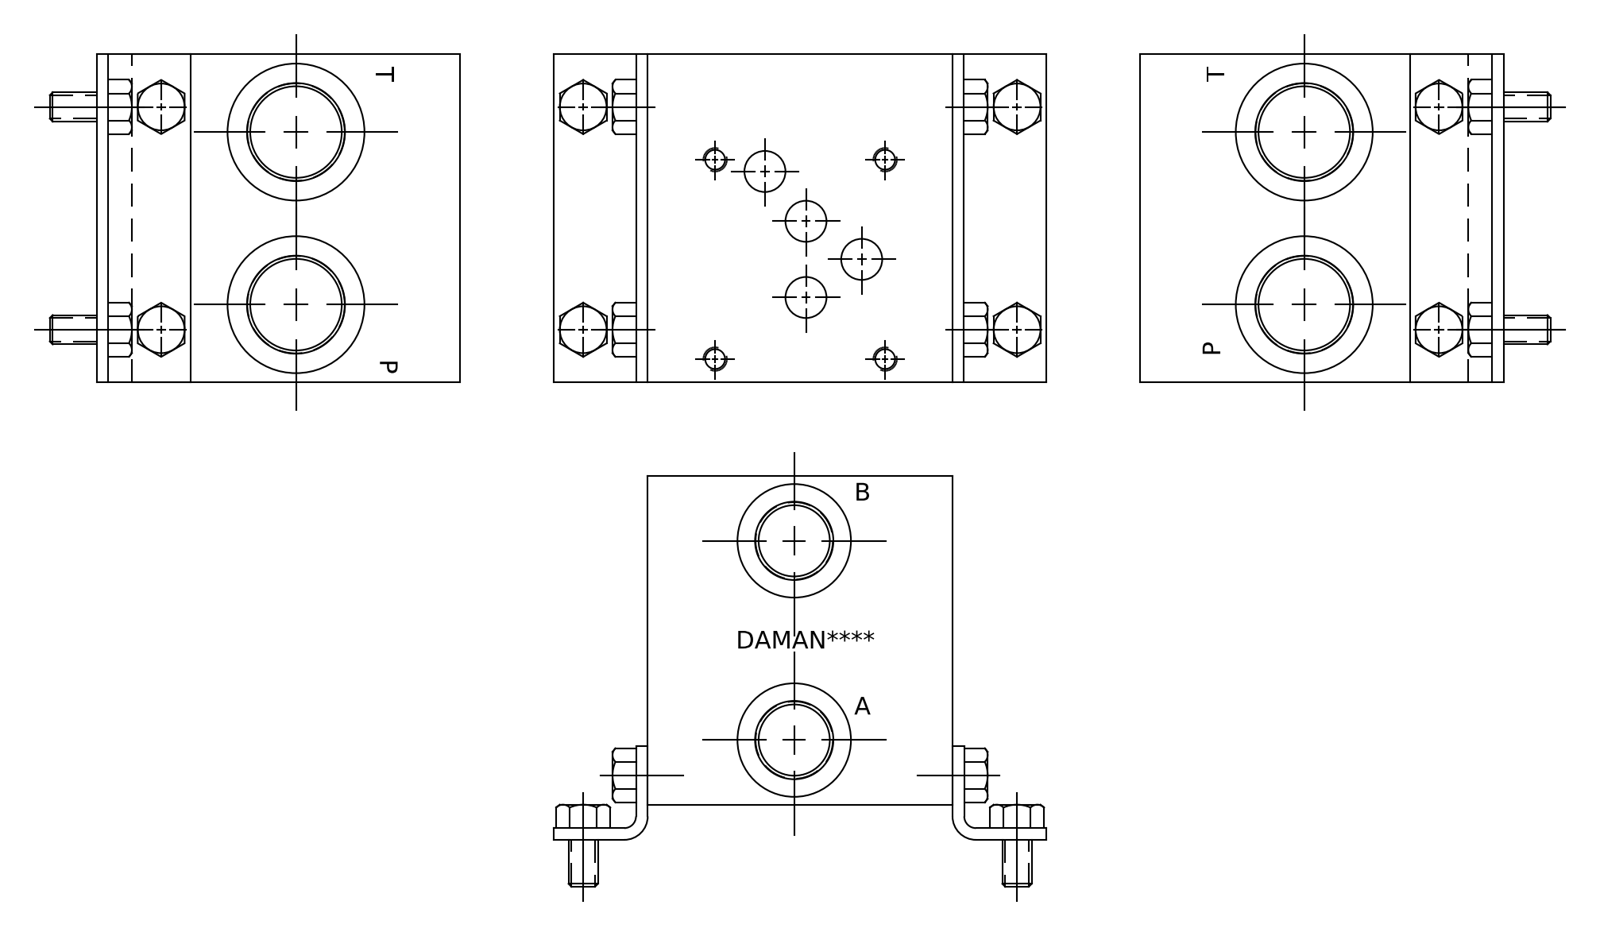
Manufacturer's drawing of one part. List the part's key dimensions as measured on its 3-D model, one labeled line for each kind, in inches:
Part name (STEP PRODUCT): AD05P013B_3D
STEP written by: Autodesk Inventor 2009 (AUTOMOTIVE_DESIGN)
Units: inches
Bodies: 1 solid, 112 faces (26 planar, 44 cylindrical, 42 other)
Overall size (bounding box): 3.5 × 3.5 × 3.25
Volume: 33.71 in³ · Surface area: 99.38 in²
Round holes (diameter × count): ⌀0.201 ×4, ⌀0.25 ×4, ⌀0.438 ×4, ⌀0.257 ×2, ⌀0.313 ×2, ⌀0.688 ×2, ⌀0.745 ×2, ⌀0.825 ×2, ⌀0.834 ×2, ⌀0.961 ×2, ⌀1.041 ×2, ⌀1.208 ×2
Main face-to-face distances: 3.5, 3.25, 0.031, 3.219, 3.188, 3.469, 0.734, 2.516, 0.703, 2.485
Hole centre spacings: 0.72, 1.069, 1.463, 1.694, 2.552, 0.546, 0.688, 0.812
